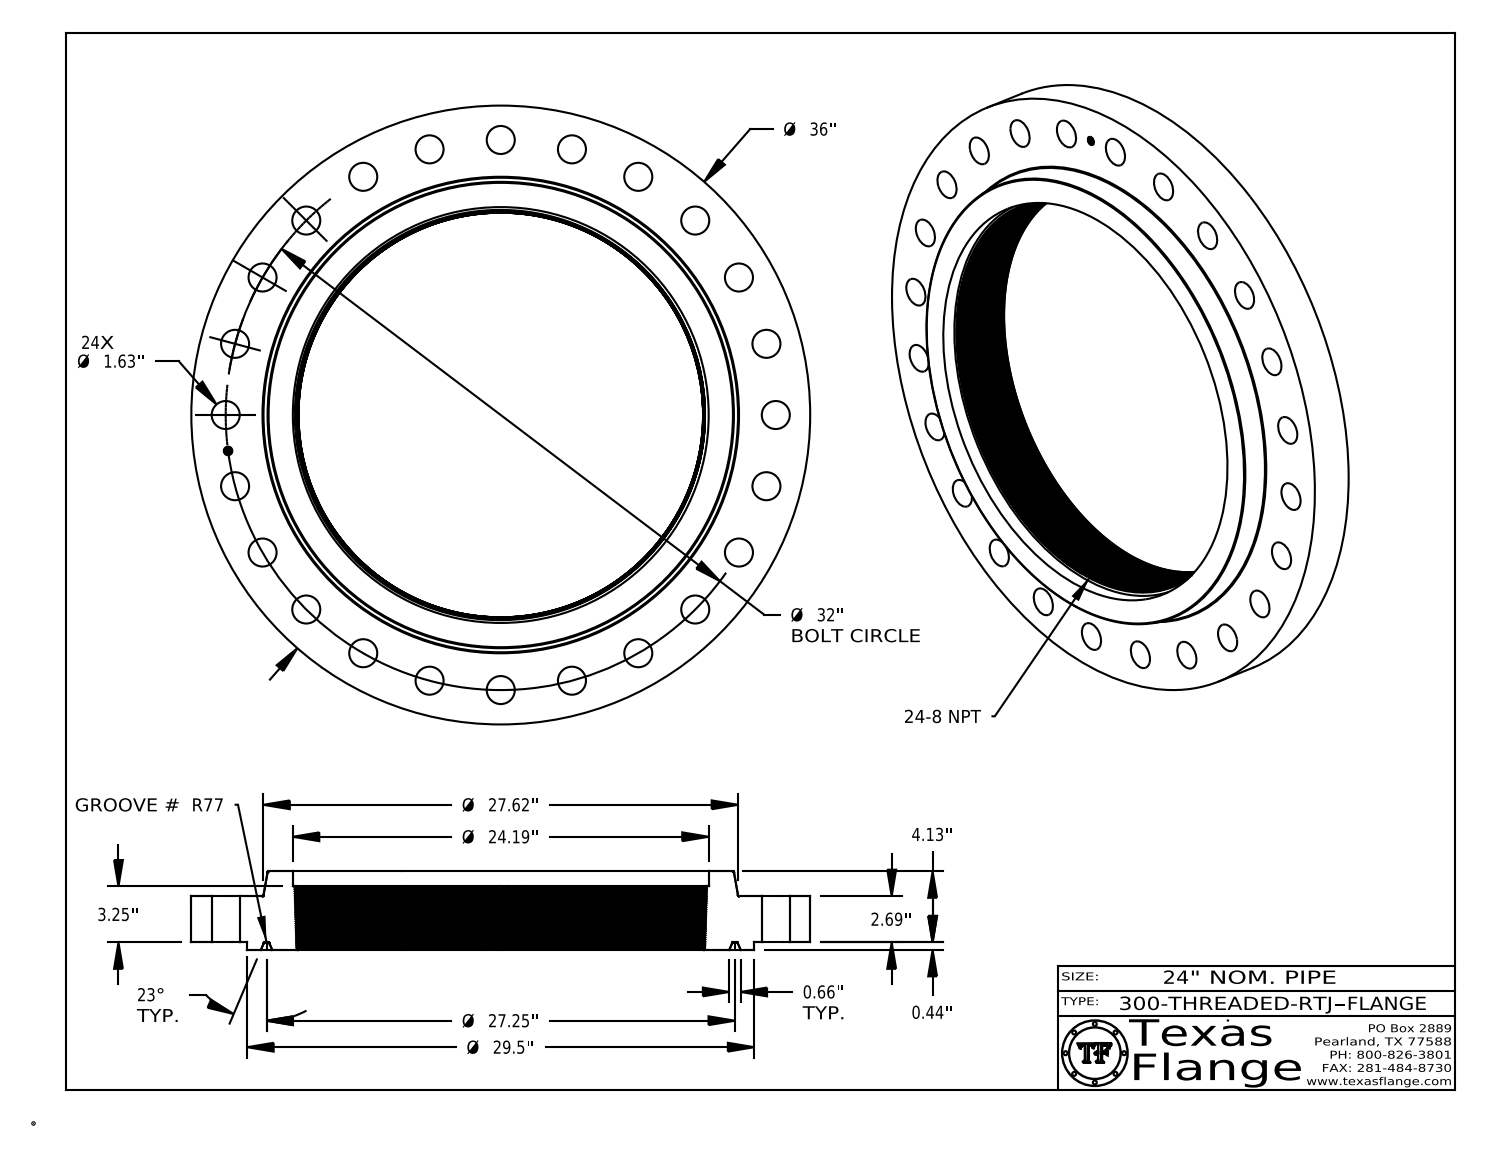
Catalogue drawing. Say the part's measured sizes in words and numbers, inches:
The part is named "300-THREADED-RTJ". Its 3-D file was written by "CATIA V5 STEP AP214 (AUTOMOTIVE_DESIGN)". It is 1 solid with 762 faces: 372 planar, 74 cylindrical and 316 other. Overall it measures 36 by 36 by 4.568 inches. Its volume is 1 694 cubic inches and its surface area 2 457 square inches. Round holes: 24 of diameter 1.63, 1 of diameter 0.495, 1 of diameter 24.19. Round bosses or shafts: 8 of diameter 0.03, 1 of diameter 36, 1 of diameter 29.5, 1 of diameter 0.39. The main face-to-face distances are 2.69, 0.437, 3.128, 4.567, 4.13, 1.44, 3.687, 3.25, 0.56, 0.88. The hole center spacings are 16, 30.909, 4.177, 8.282, 12.246, 19.48, 22.627, 25.387.
